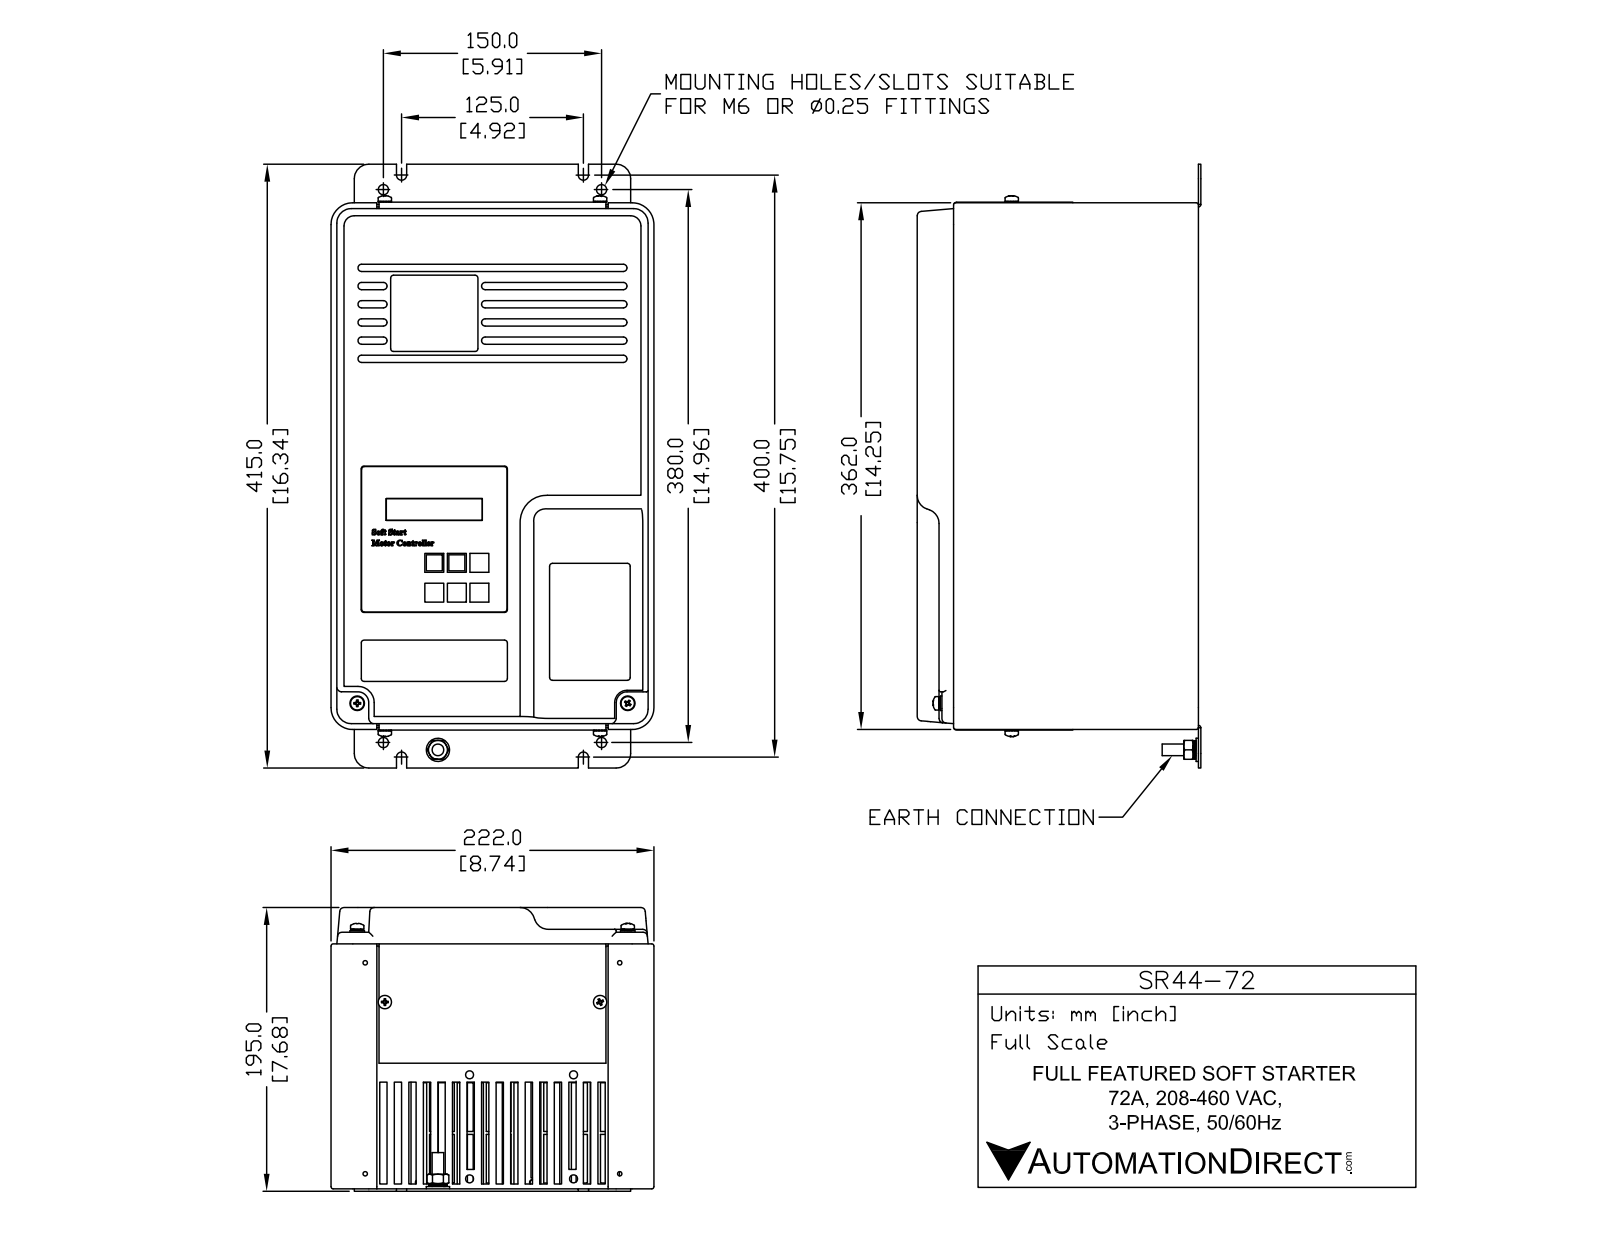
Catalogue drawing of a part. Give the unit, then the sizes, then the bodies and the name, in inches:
Units: inches
Overall size (bounding box): 16.339 × 8.74 × 7.665
Round holes (diameter × count): ⌀0.276 ×4
Round bosses / shafts (diameter × count): ⌀0.394 ×4, ⌀0.63 ×1, ⌀0.315 ×1
Partial cylindrical surfaces — rounded edges, fillets, slot ends (radius × count): R0.098 ×30, R0.094 ×28, R0.098 ×12, R0.059 ×11, R0.118 ×8, R0.394 ×8, R0.079 ×6, R0.138 ×4
Main face-to-face distances: 0.401, 0.802, 1.204, 1.605, 2.006, 2.407, 2.808, 0.232, 3.209, 8.508
Hole centre spacings: 5.906, 14.961, 16.084
Volume: 502.3 in³ · Surface area: 1 102 in²
Bodies: 1 solid, 768 faces (455 planar, 175 cylindrical, 138 other)
Part name (STEP PRODUCT): SR44-72
STEP written by: SolidWorks 2013 (AUTOMOTIVE_DESIGN)
